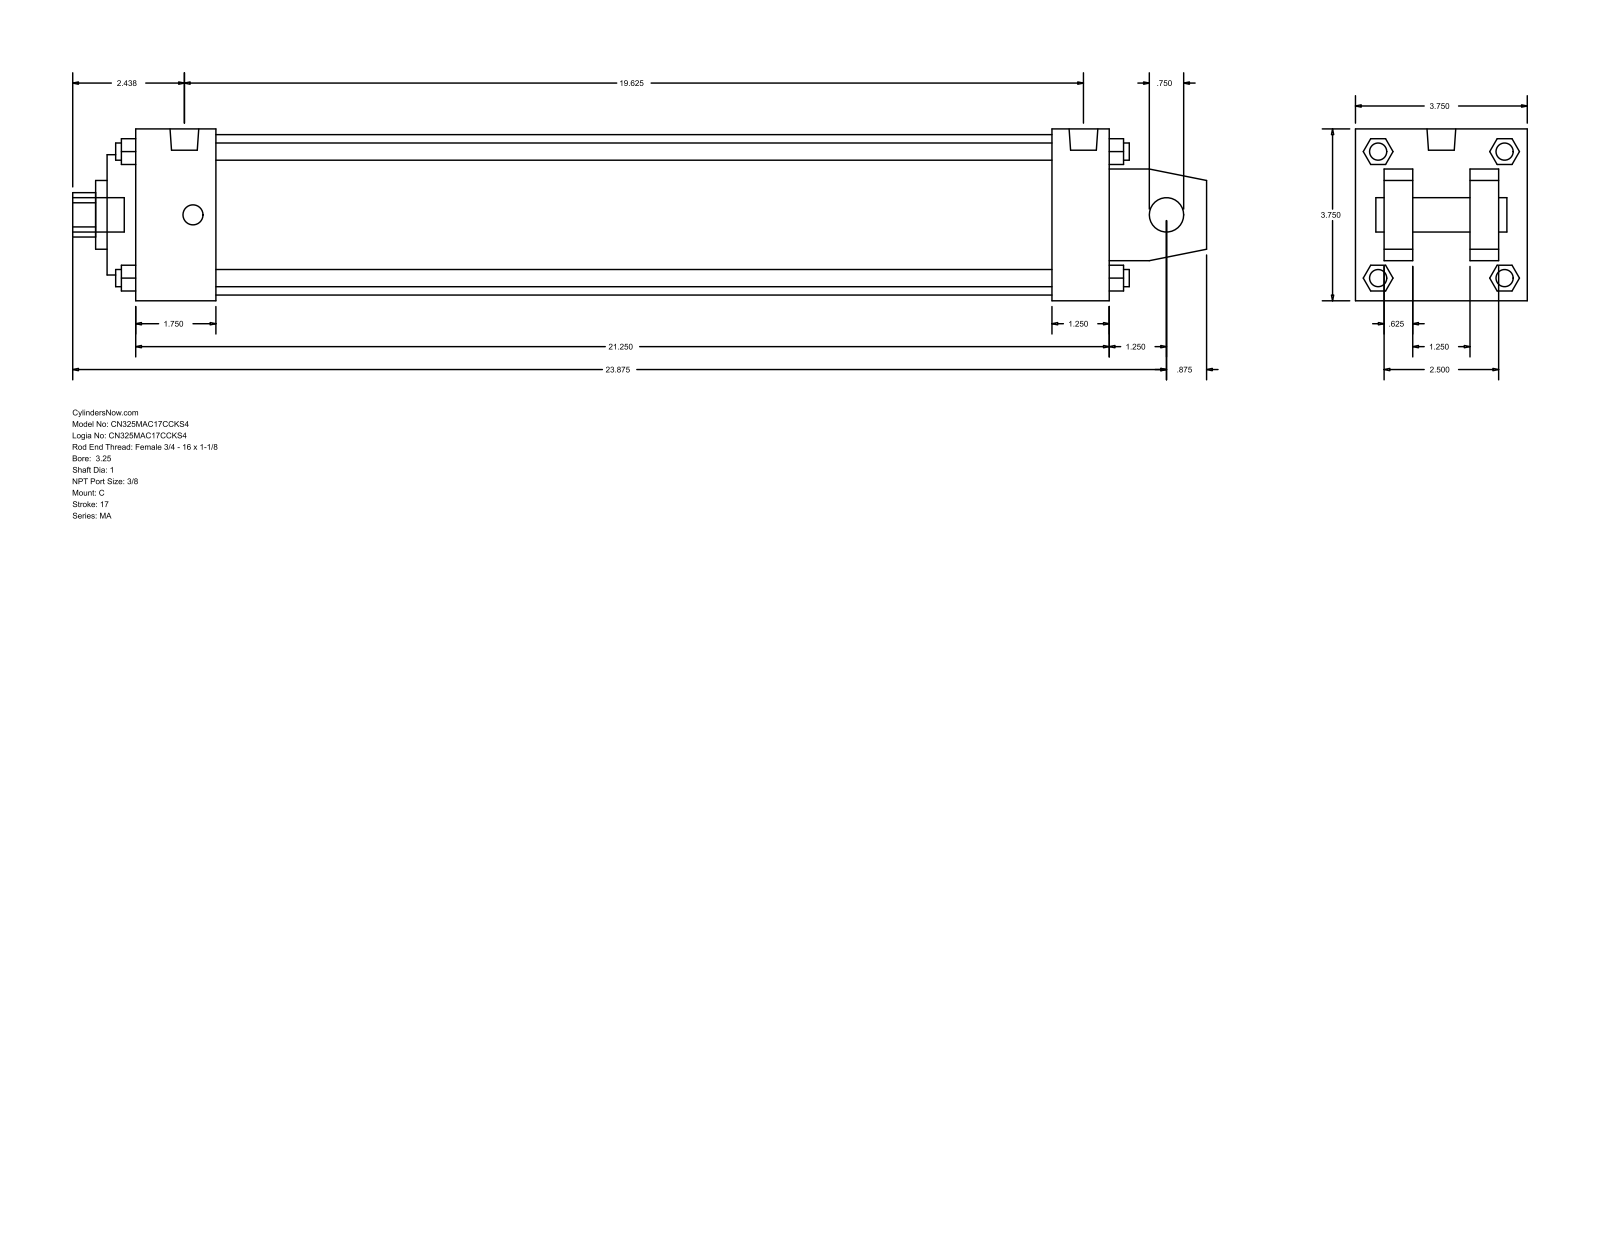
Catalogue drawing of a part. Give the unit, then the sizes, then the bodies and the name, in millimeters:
Units: millimetres
Overall size (bounding box): 628.65 × 95.25 × 95.25
Round holes (diameter × count): ⌀19.05 ×1, ⌀25.4 ×1, ⌀38.1 ×1, ⌀66.67 ×1, ⌀88.9 ×1
Round bosses / shafts (diameter × count): ⌀11.11 ×4, ⌀9.53 ×4, ⌀15.93 ×2, ⌀19.05 ×1
Partial cylindrical surfaces — rounded edges, fillets, slot ends (radius × count): R12.29 ×1
Main face-to-face distances: 95.24, 15.87, 63.5, 539.75, 31.74, 79.37, 47.63, 555.62, 508, 31.75
Bodies: 0 solids, 141 faces (109 planar, 32 cylindrical, 0 other)
Part name (STEP PRODUCT): MA_C__0325_1
STEP written by: GSSL Pune (CONFIG_CONTROL_DESIGN)
